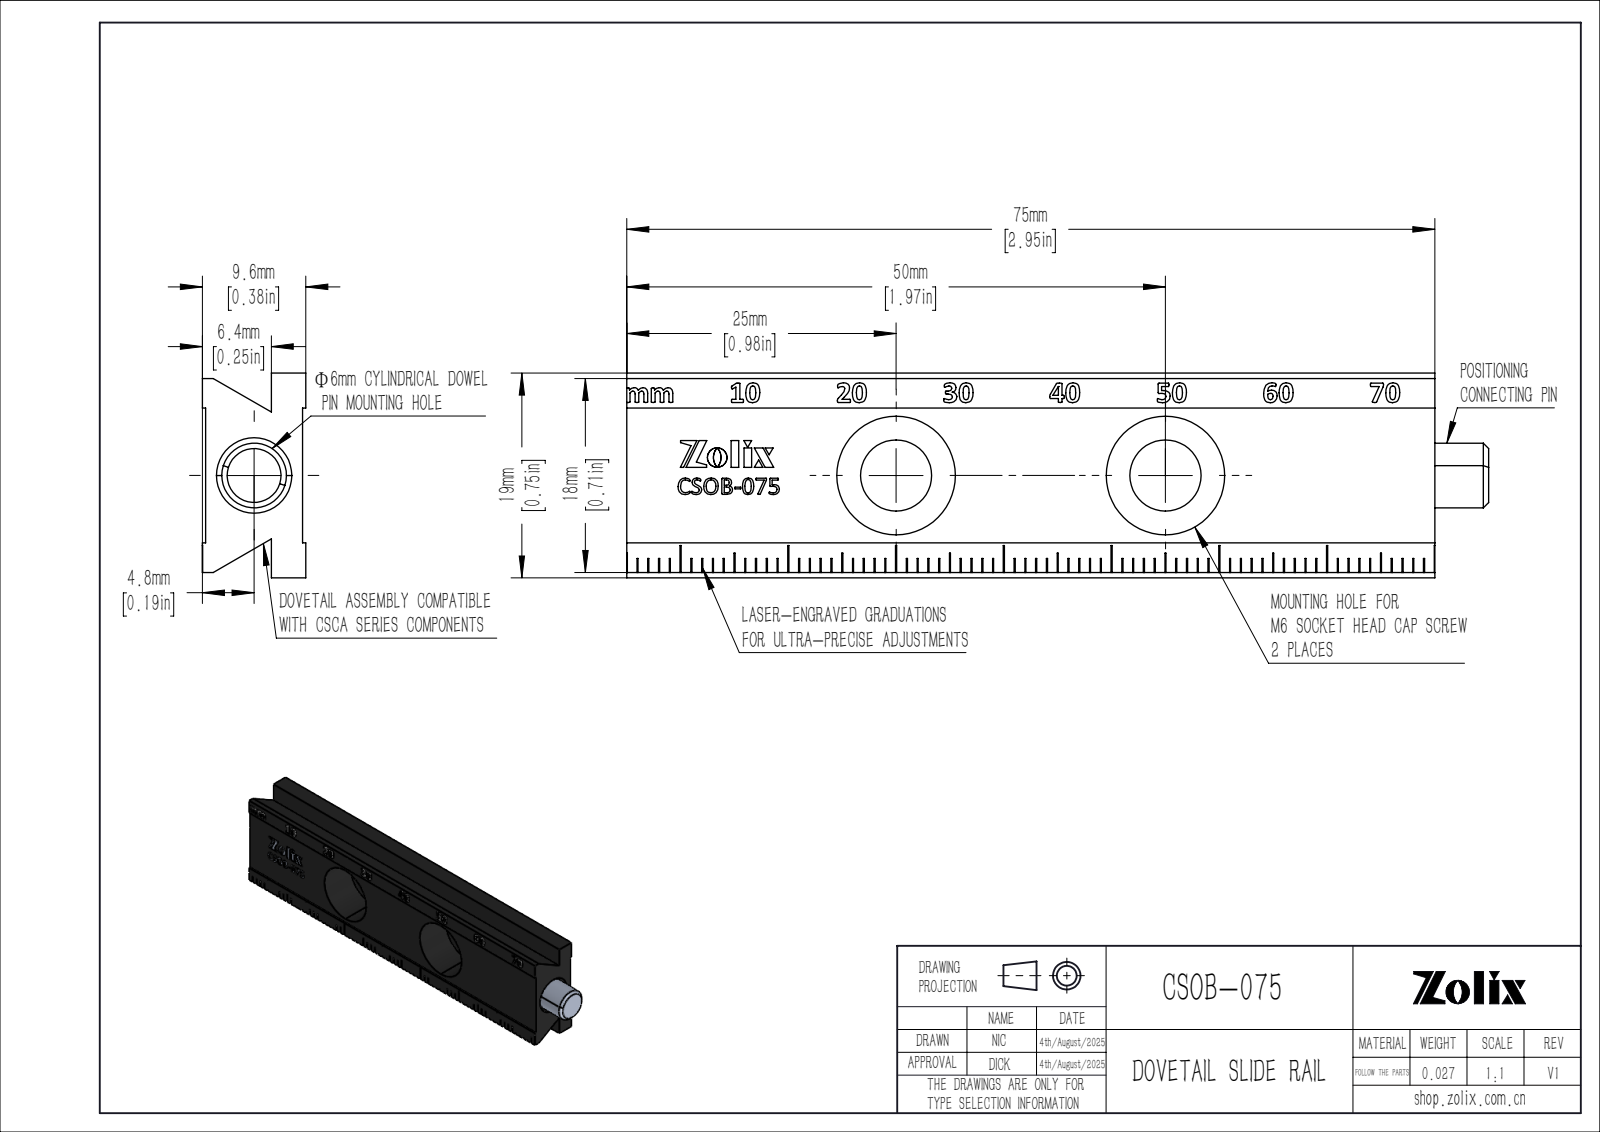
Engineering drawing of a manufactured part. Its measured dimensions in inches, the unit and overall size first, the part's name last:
Units: inches
Overall size (bounding box): 3.15 × 0.748 × 0.378
Round holes (diameter × count): ⌀0.26 ×2, ⌀0.433 ×2, ⌀0.236 ×1
Main face-to-face distances: 0.366, 0.354, 0.24, 0.114, 0.126, 0.252, 0.378, 0.748, 0.02, 0.728
Hole centre spacings: 0.984
Volume: 0.602 in³ · Surface area: 9.525 in²
Bodies: 2 solids, 652 faces (555 planar, 14 cylindrical, 83 other)
Part name (STEP PRODUCT): CSOB-075
STEP written by: SolidWorks 2020 (CONFIG_CONTROL_DESIGN)
